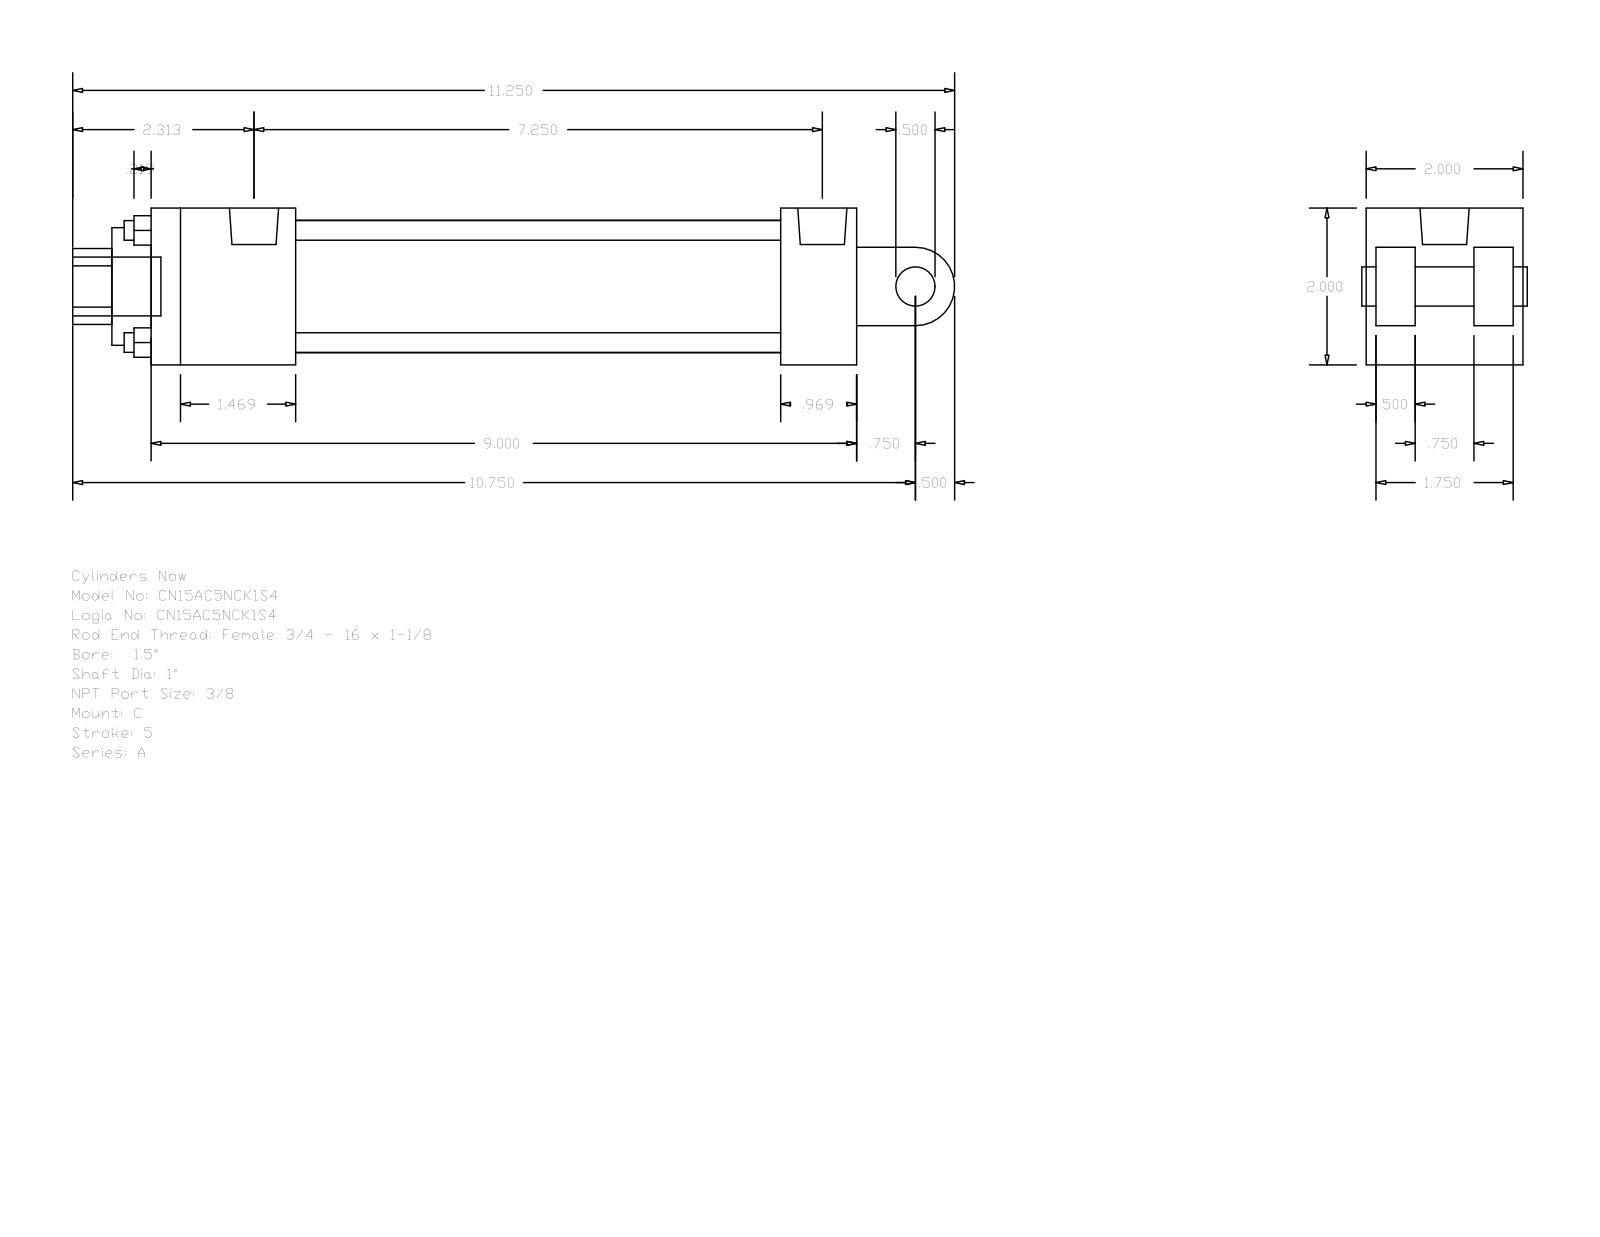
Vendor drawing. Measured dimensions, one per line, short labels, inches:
name: A_C__0150_1
written by: GSSL Pune (CONFIG_CONTROL_DESIGN)
unit: in
bodies: 0 solids, 99 faces (70 planar, 29 cylindrical, 0 other)
size: 11.25 × 2 × 2
holes: 4× ⌀0.25, 2× ⌀0.219, 1× ⌀0.627, 1× ⌀1, 1× ⌀1.5, 1× ⌀1.69
bosses: 2× ⌀0.219, 1× ⌀0.75, 1× ⌀0.627, 1× ⌀0.5
rounds: 1× R0.484, 1× R0.5
face distances: 2, 0.5, 0.125, 0.625, 1.375, 1.875, 1.25, 9, 8.031, 0.969
hole spacings: 1.011, 1.43, 2.022, 0.156
